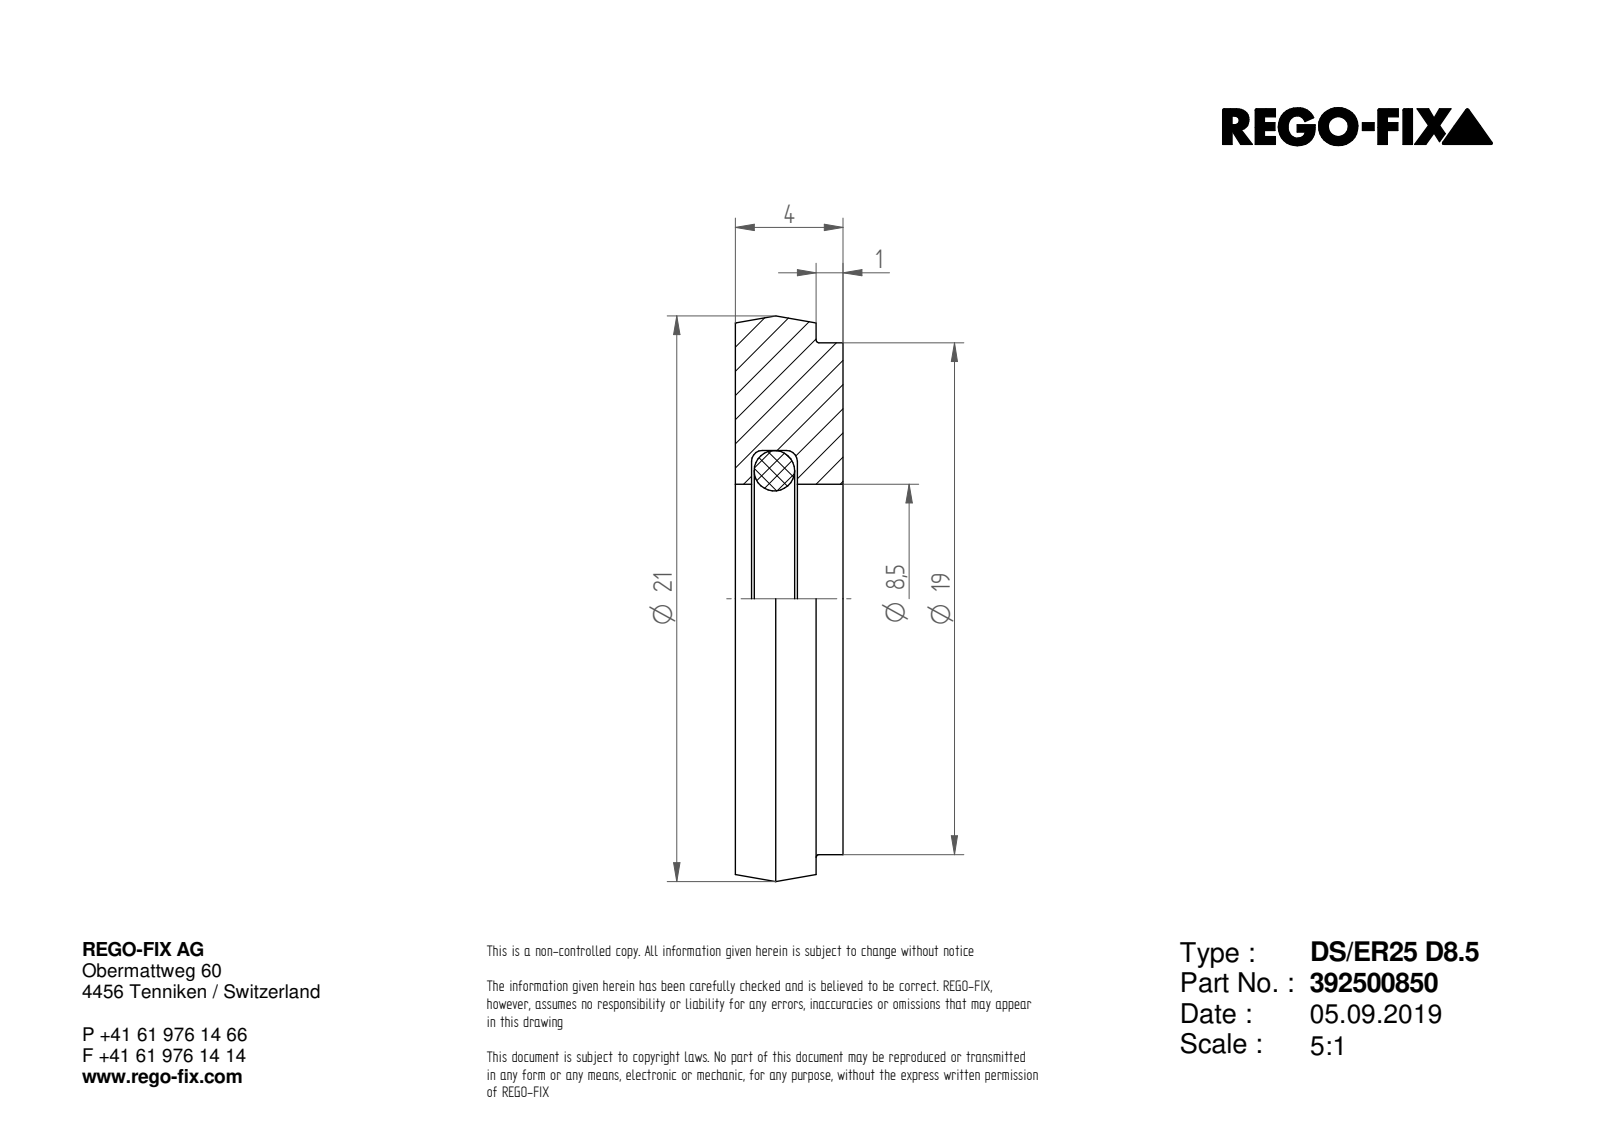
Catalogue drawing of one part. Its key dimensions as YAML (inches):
part_name: "NOCUT"
step_written_by: "SIEMENS PLM Software Solid Edge ST10 (AUTOMOTIVE_DESIGN)"
units: inches
bodies: {solids: 1, faces: 7, planar: 3, cylindrical: 3, other: 1}
overall_size: [0.827, 0.827, 0.157]
volume: 0.067
surface_area: 1.46
round_holes:
  - {diameter: 0.335, count: 1}
round_bosses_or_shafts:
  - {diameter: 0.827, count: 1}
  - {diameter: 0.748, count: 1}
face_to_face_distances: [0.157, 0.039, 0.118]
